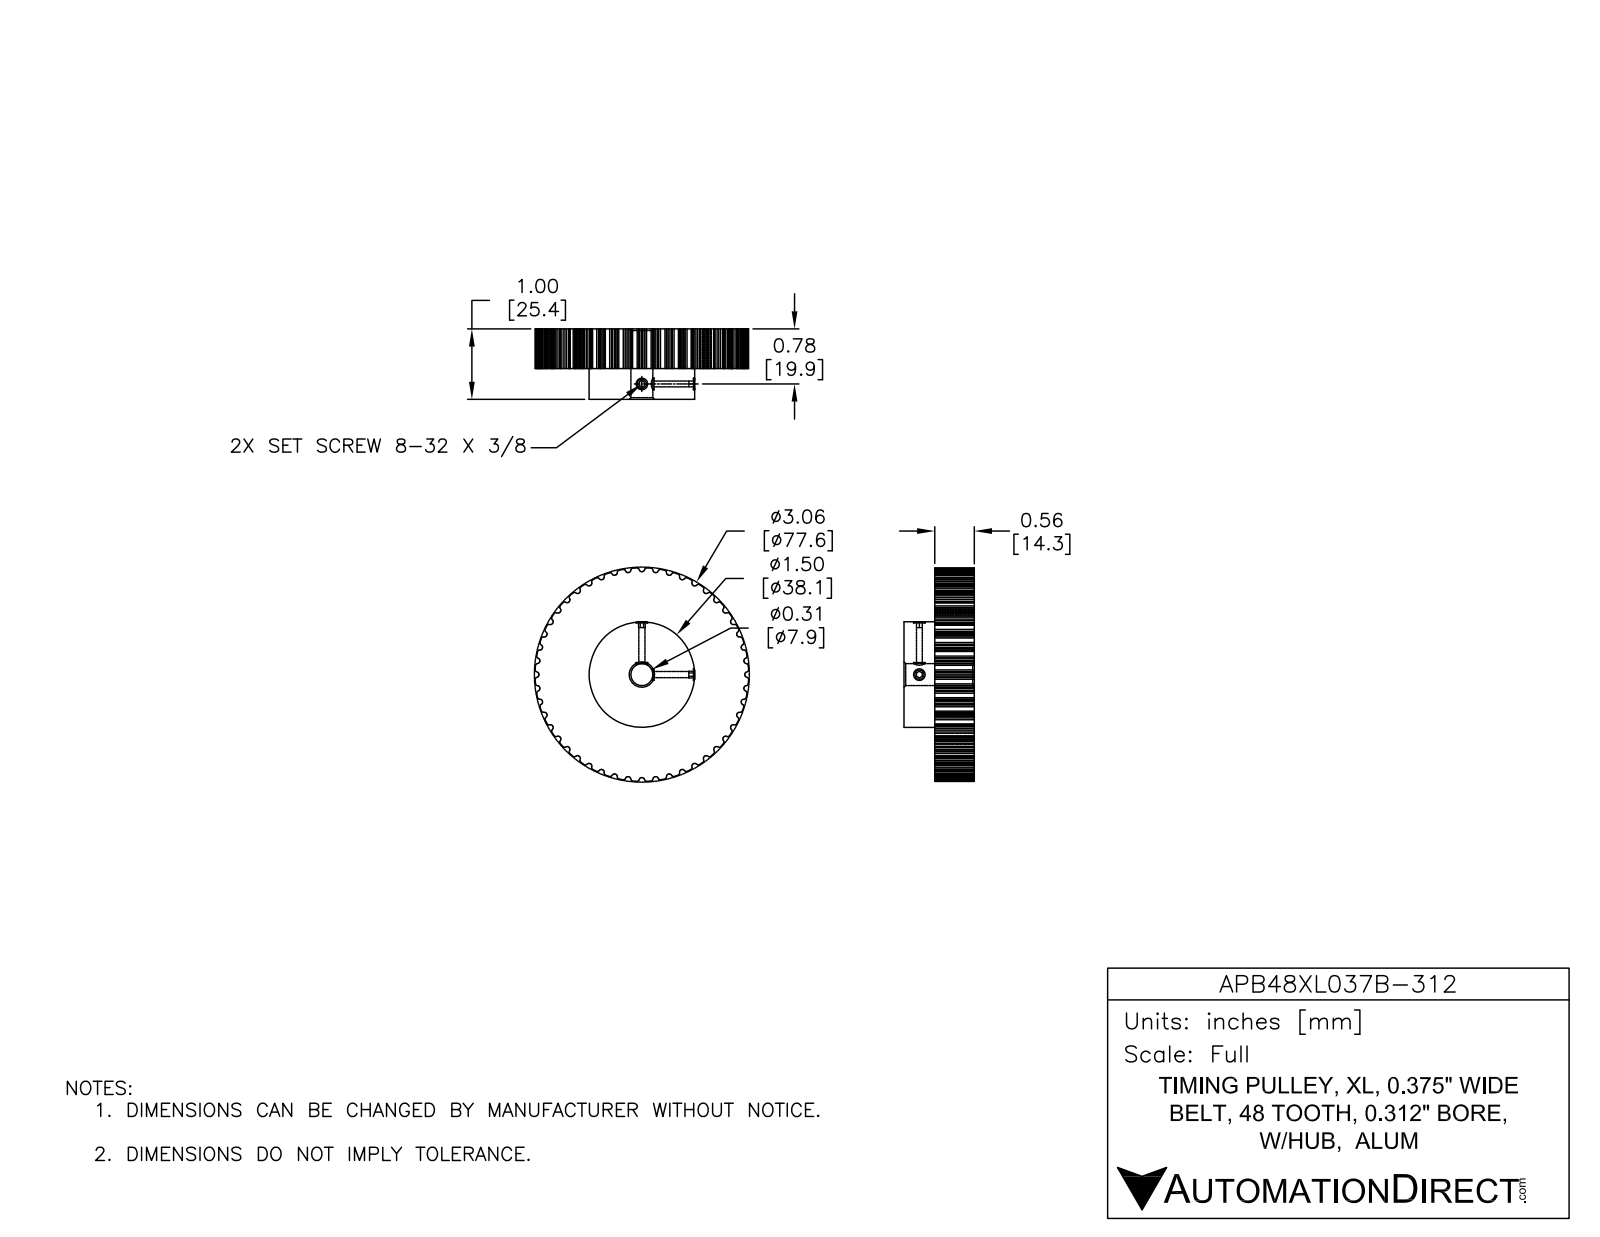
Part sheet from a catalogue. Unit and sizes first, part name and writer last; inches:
Units: inches
Overall size (bounding box): 3.036 × 3.036 × 1
Round holes (diameter × count): ⌀0.088 ×2, ⌀0.313 ×1
Round bosses / shafts (diameter × count): ⌀1.5 ×1
Partial cylindrical surfaces — rounded edges, fillets, slot ends (radius × count): R0.015 ×192, R1.463 ×1, R1.518 ×1
Main face-to-face distances: 0.56, 1, 0.44, 1.191, 1.19, 1.189, 1.192, 1.191
Volume: 4.634 in³ · Surface area: 24.17 in²
Bodies: 1 solid, 442 faces (99 planar, 333 cylindrical, 10 other)
Part name (STEP PRODUCT): APB48XL037B-312
STEP written by: SolidWorks 2014 (AUTOMOTIVE_DESIGN)
